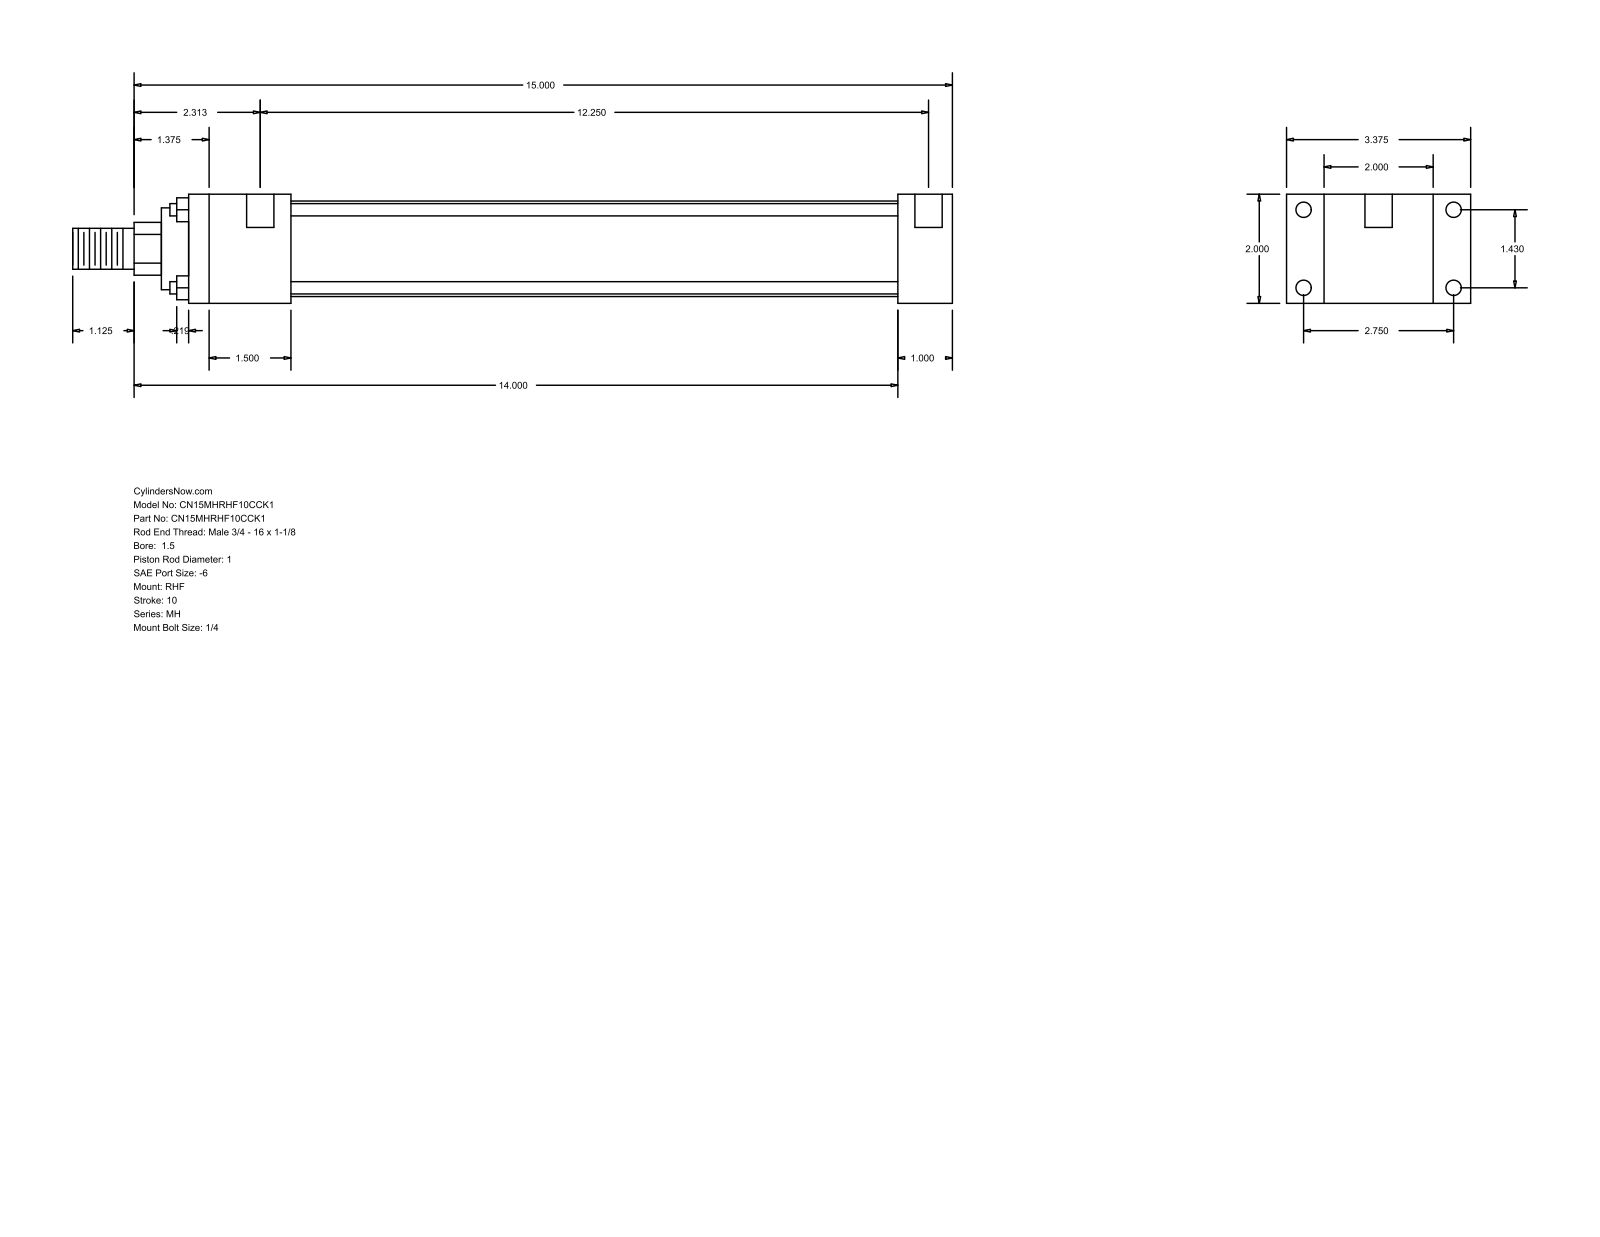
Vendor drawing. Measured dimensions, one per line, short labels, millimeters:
name: MH_RHF__0150_1
written by: GSSL Pune (CONFIG_CONTROL_DESIGN)
unit: mm
bodies: 0 solids, 88 faces (60 planar, 28 cylindrical, 0 other)
size: 409.57 × 85.72 × 50.8
holes: 4× ⌀5.56, 4× ⌀7.14, 2× ⌀12.7
bosses: 4× ⌀5.71, 1× ⌀44.45, 1× ⌀38.1, 1× ⌀25.4, 1× ⌀19.05
rounds: 1× R12.29
face distances: 50.8, 25.4, 17.46, 68.26, 85.72, 355.6, 330.2, 47.63, 282.57, 307.97
hole spacings: 36.32, 69.84, 78.72, 314.33, 3.18, 311.15
